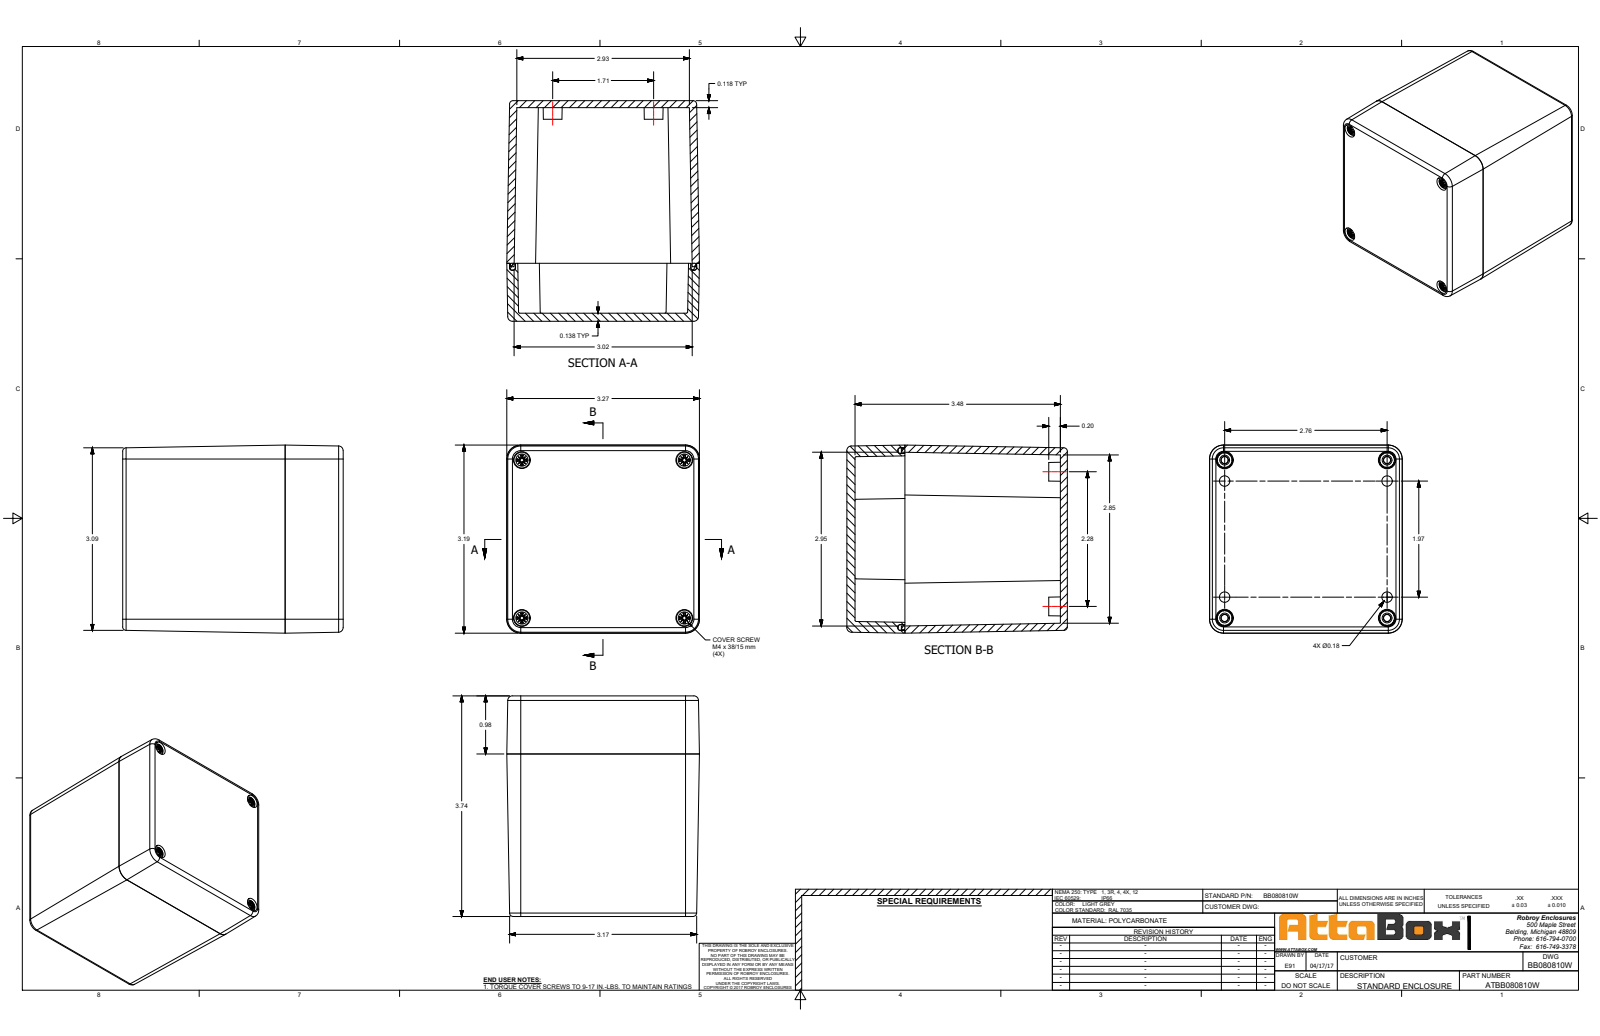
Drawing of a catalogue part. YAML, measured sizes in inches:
part_name: "BB080810W"
step_written_by: "SolidWorks 2018 (AUTOMOTIVE_DESIGN)"
units: inches
bodies: {solids: 11, faces: 1607, planar: 603, cylindrical: 452, other: 552}
overall_size: [3.74, 3.268, 3.189]
volume: 9.686
surface_area: 170.8
round_holes:
  - {diameter: 0.128, count: 4}
  - {diameter: 0.177, count: 4}
  - {diameter: 0.193, count: 4}
  - {diameter: 0.197, count: 4}
  - {diameter: 0.201, count: 4}
  - {diameter: 0.276, count: 4}
  - {diameter: 0.287, count: 4}
  - {diameter: 0.295, count: 4}
round_bosses_or_shafts:
  - {diameter: 0.268, count: 4}
  - {diameter: 0.173, count: 4}
  - {diameter: 0.157, count: 4}
  - {diameter: 0.13, count: 4}
partial_cylinders:
  - {radius: 0.039, count: 32}
  - {radius: 0.012, count: 24}
  - {radius: 0.02, count: 8}
  - {radius: 0.098, count: 8}
  - {radius: 0.197, count: 8}
  - {radius: 0.059, count: 4}
  - {radius: 0.079, count: 4}
  - {radius: 0.102, count: 4}
face_to_face_distances: [0.122, 3.74, 0.124, 0.118, 3.622, 0.138, 3.602, 3.484, 3.189, 3.067]
hole_center_spacings: [0.354, 2.323, 2.756, 2.779, 3.604, 1.969, 2.677, 3.387]
